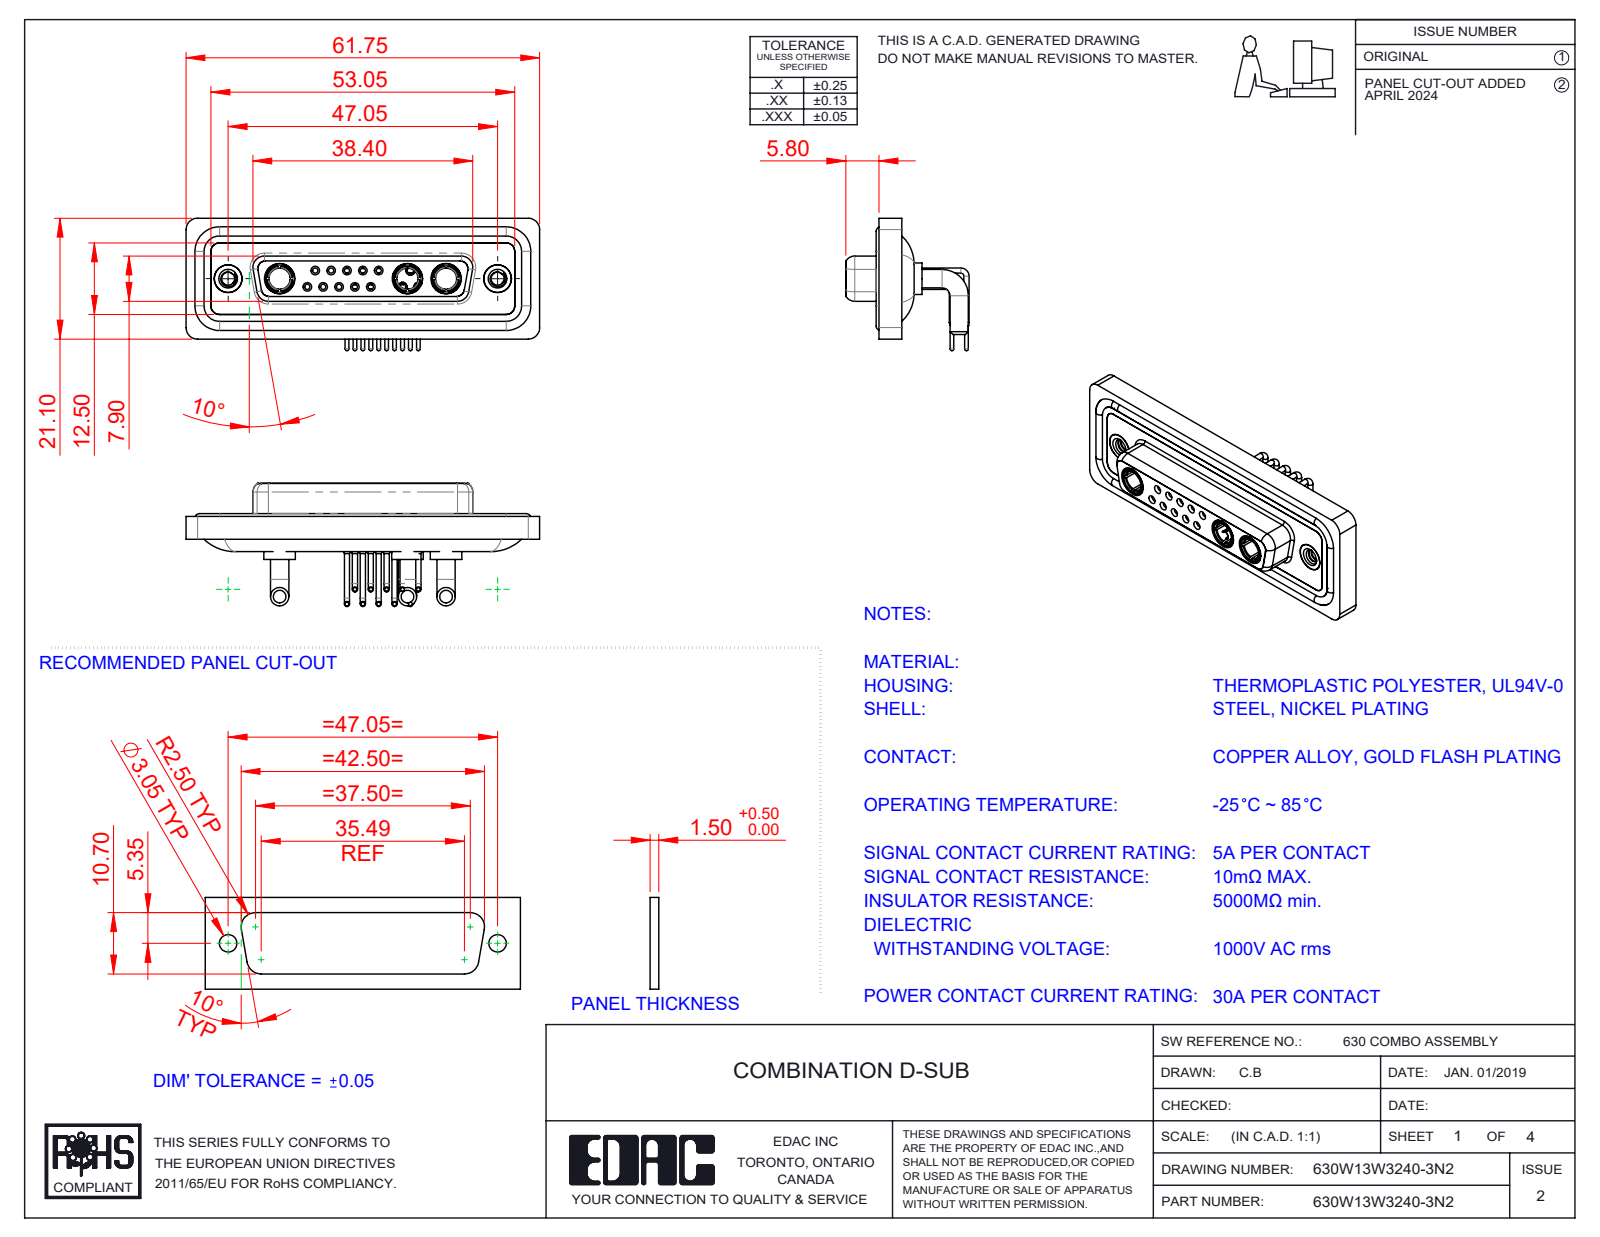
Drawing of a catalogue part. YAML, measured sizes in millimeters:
part_name: "630W13W3140-3N2; 630Combo Contact Row 1_50 Contacts; 630Combo Housing_13W3; 630Combo Shell Rear_25 Contacts (+5 more)"
step_written_by: "SolidWorks 2023 (CONFIG_CONTROL_DESIGN)"
units: millimeters
bodies: {solids: 23, faces: 1150, planar: 342, cylindrical: 493, other: 315}
overall_size: [61.75, 23.12, 21.53]
volume: 8554
surface_area: 14351
round_holes:
  - {diameter: 0.9, count: 10}
  - {diameter: 1.1, count: 10}
  - {diameter: 1.5, count: 10}
  - {diameter: 2, count: 10}
  - {diameter: 1.6, count: 5}
  - {diameter: 1.7, count: 5}
  - {diameter: 4.85, count: 5}
  - {diameter: 3.7, count: 3}
  - {diameter: 5.3, count: 3}
  - {diameter: 2.26, count: 2}
  - {diameter: 4, count: 2}
  - {diameter: 4.05, count: 2}
round_bosses_or_shafts:
  - {diameter: 0.9, count: 15}
  - {diameter: 1.6, count: 12}
  - {diameter: 0.65, count: 10}
  - {diameter: 3.2, count: 6}
  - {diameter: 2, count: 5}
  - {diameter: 1.5, count: 5}
  - {diameter: 5.5, count: 3}
  - {diameter: 5.2, count: 3}
partial_cylinders:
  - {radius: 1.5, count: 18}
  - {radius: 2, count: 18}
  - {radius: 1.35, count: 8}
  - {radius: 1.6, count: 8}
  - {radius: 0.25, count: 4}
  - {radius: 0.5, count: 4}
  - {radius: 0.6, count: 4}
  - {radius: 0.65, count: 4}
face_to_face_distances: [0.4, 1.8, 4.1, 1.1, 1.6, 3.1, 2.5, 1.5, 3.7, 1.4]
hole_center_spacings: [3.16, 2.77, 5.54, 5.04, 8.31, 5.03, 7.49, 11.08]
